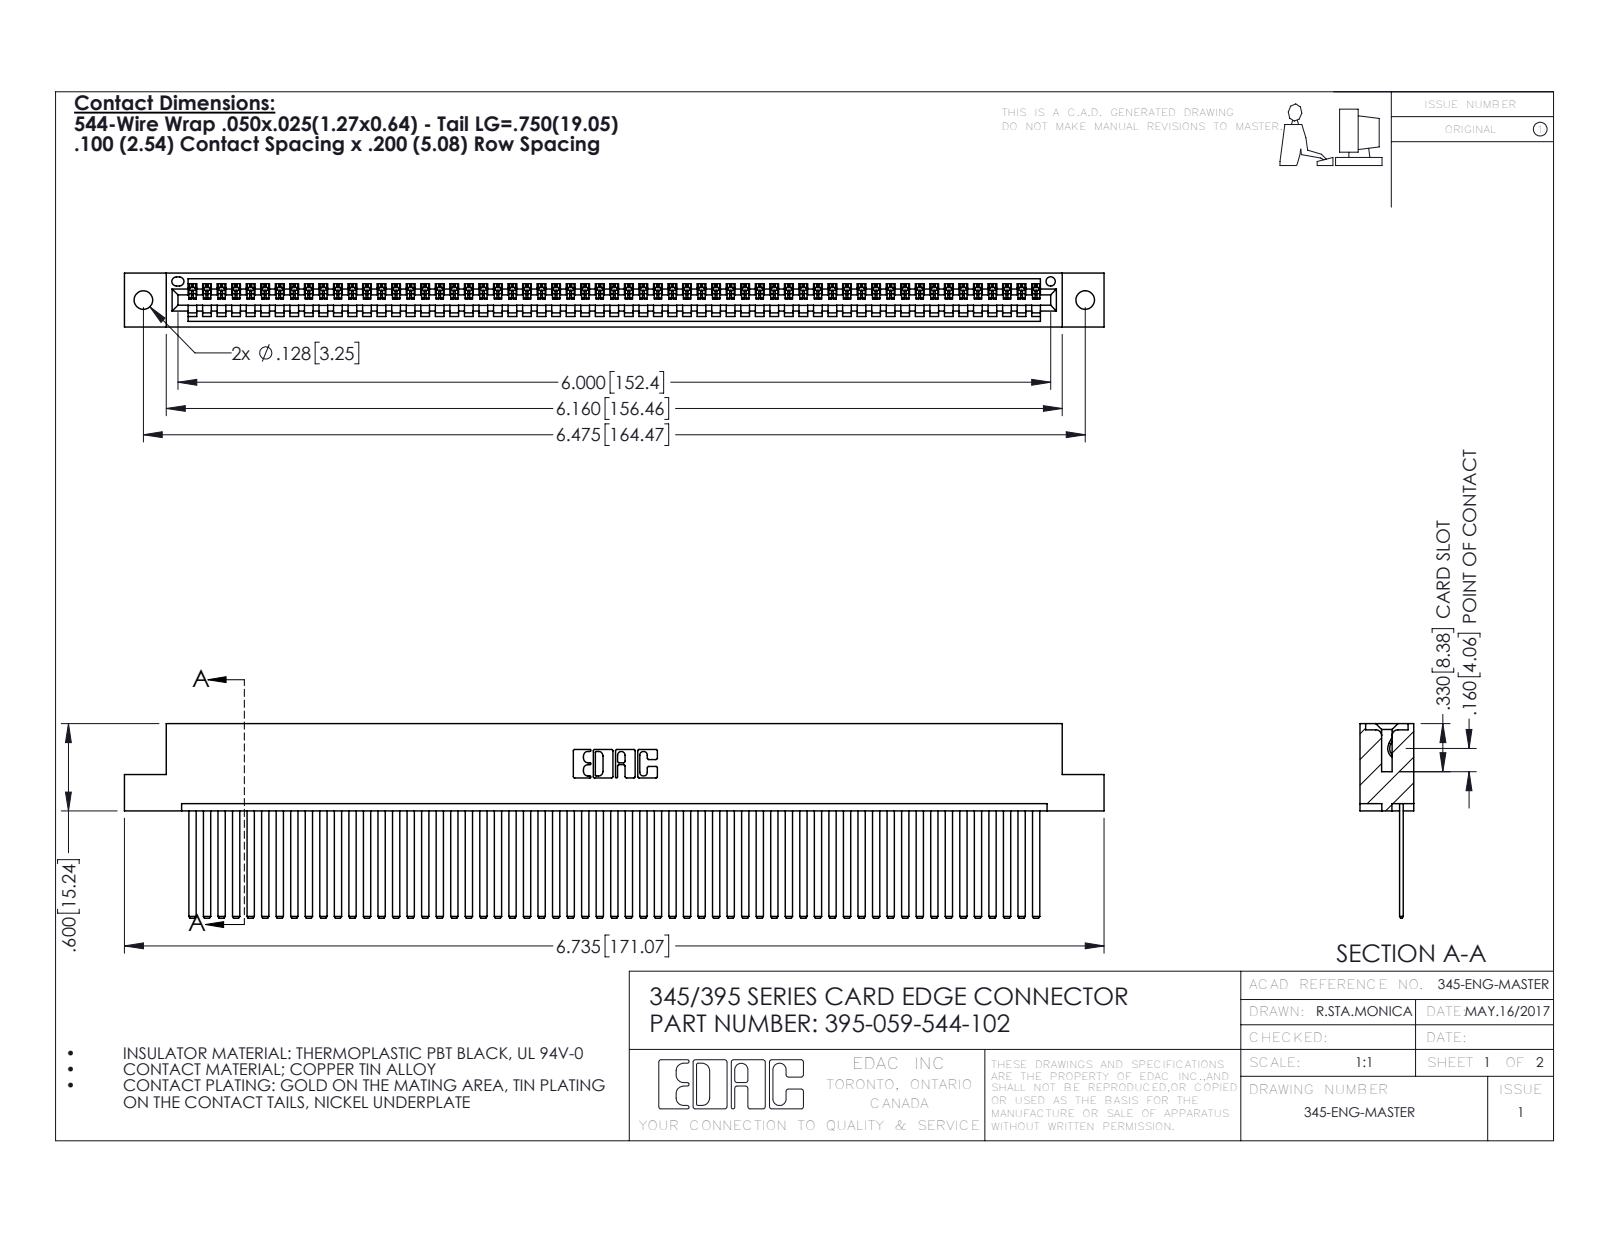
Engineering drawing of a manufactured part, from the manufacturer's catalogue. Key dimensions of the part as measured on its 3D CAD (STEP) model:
Part name (STEP PRODUCT): 395-059-544-102; 345-292-001_345-293-144; 345 Part_Flush Mounting Lugs - 0.128 Dia
STEP written by: SolidWorks 2016 (CONFIG_CONTROL_DESIGN)
Units: inches
Bodies: 60 solids, 3194 faces (2204 planar, 990 cylindrical, 0 other)
Overall size (bounding box): 6.735 × 1.337 × 0.37
Volume: 1.039 in³ · Surface area: 38.2 in²
Round holes (diameter × count): ⌀0.128 ×2, ⌀0.064 ×1
Partial cylindrical surfaces — rounded edges, fillets, slot ends (radius × count): R0.006 ×118, R0.01 ×22, R0.007 ×6, R0.031 ×6, R0.026 ×3, R0.031 ×2, R0.04 ×2, R0.014 ×1
Main face-to-face distances: 0.072, 0.298, 0.025, 0.098, 0.272, 0.37, 0.2, 0.225, 0.149, 0.072
Hole centre spacings: 0.27, 6.239, 6.475
